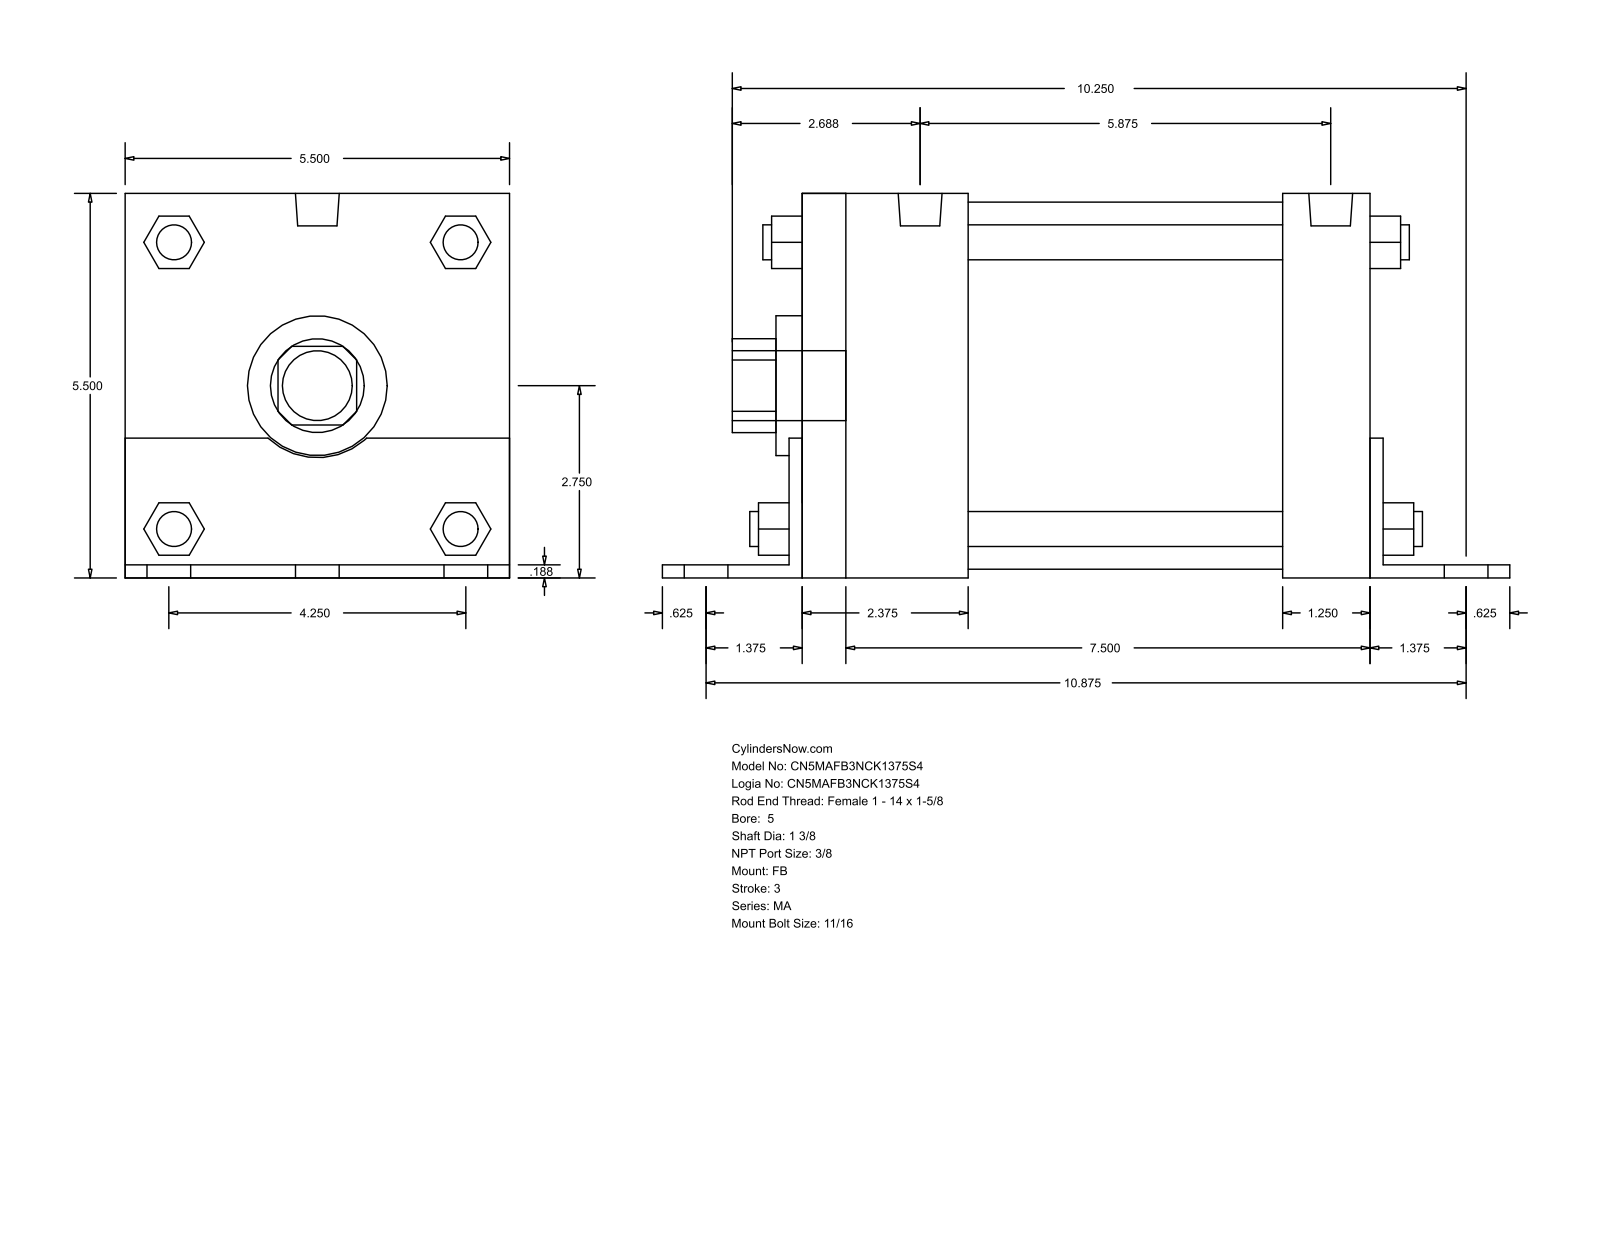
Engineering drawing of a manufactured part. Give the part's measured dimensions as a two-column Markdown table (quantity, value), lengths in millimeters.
| quantity | value |
| --- | --- |
| part name | MA_FB__0500_1.375 |
| STEP written by | GSSL Pune (CONFIG_CONTROL_DESIGN) |
| units | millimeters |
| bodies | 0 solids, 140 faces (105 planar, 35 cylindrical, 0 other) |
| overall size | 307.98 × 139.75 × 139.7 |
| round holes (diameter × count) | 34.92 × 1, 50.8 × 1, 133.35 × 1 |
| round bosses / shafts (diameter × count) | 17.46 × 6, 12.7 × 4, 11.11 × 4, 15.93 × 2, 25.4 × 1 |
| partial cylindrical surfaces (radius × count) | 17.06 × 1, 26.16 × 1 |
| main face-to-face distances | 139.7, 4.76, 139.75, 211.14, 4.71, 134.99, 206.38, 215.9, 31.75, 36.51 |
